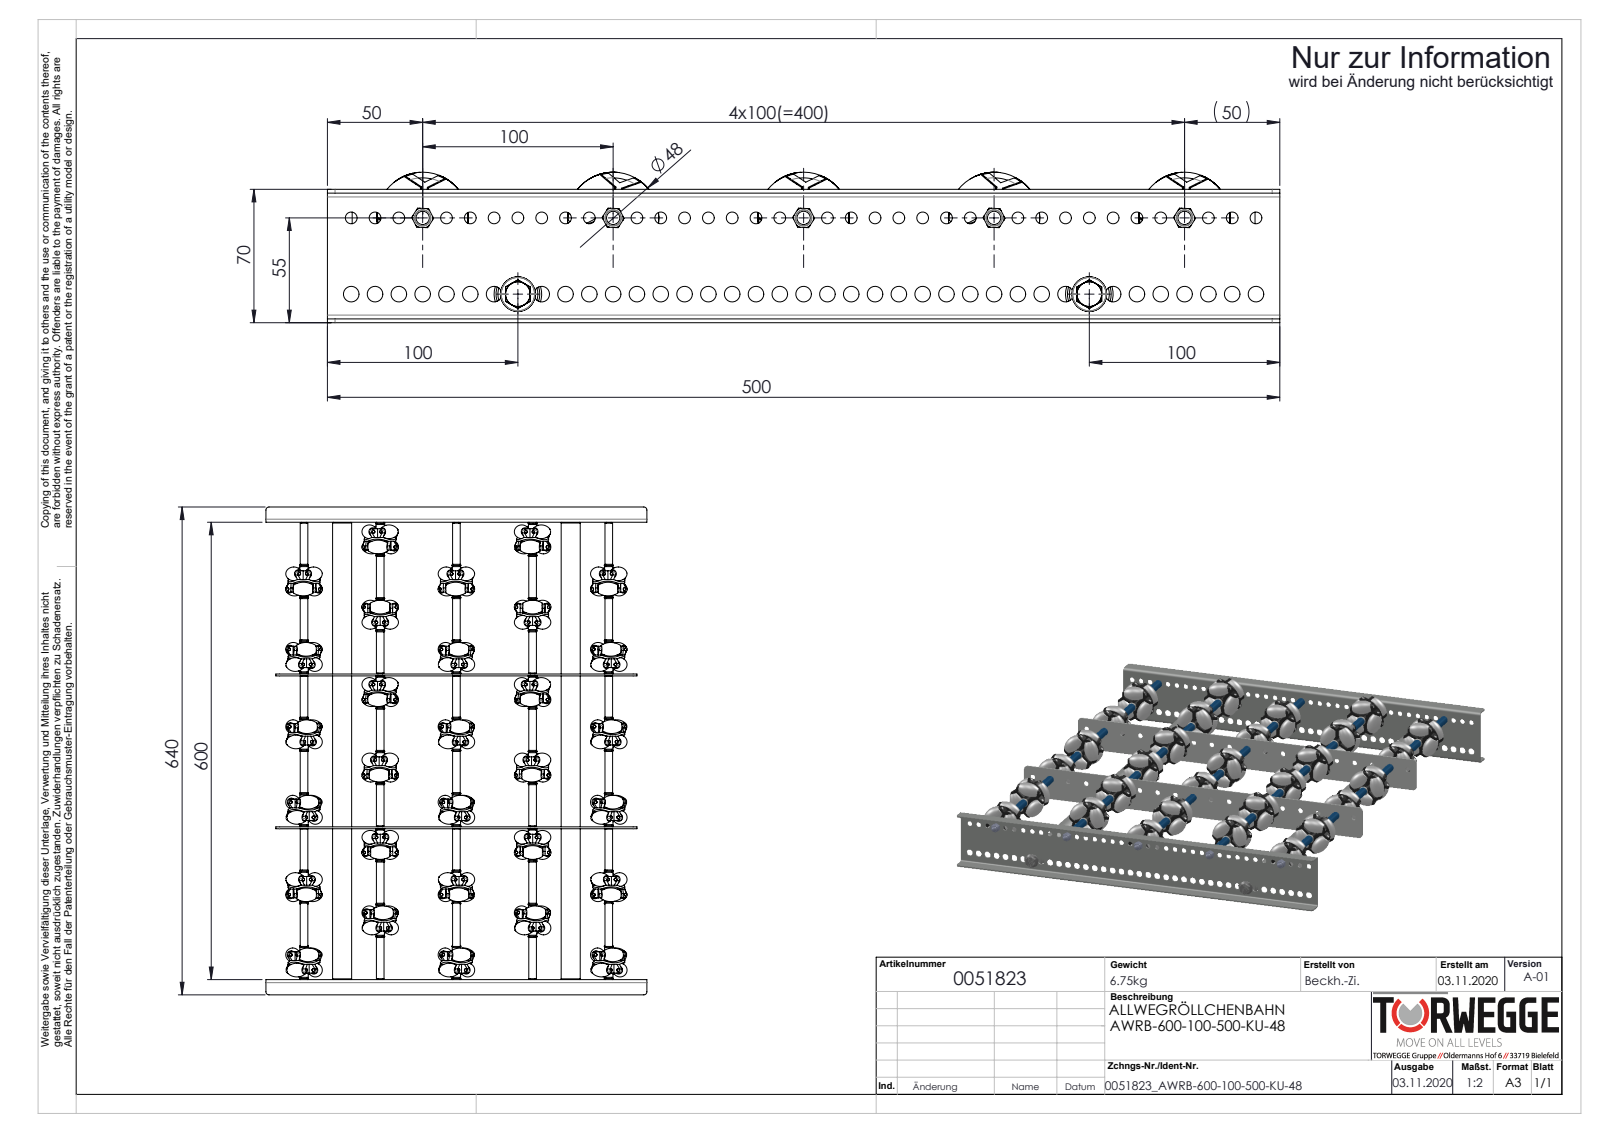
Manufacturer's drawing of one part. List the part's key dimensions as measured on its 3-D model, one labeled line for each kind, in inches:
Part name (STEP PRODUCT): AWR48_Röllchen; 0019730_Tragrollenrohr-Ø10x1,75KU_KFG_0019730_L=54; 0051823; AWR-Achse-für-Konfiguration_L600 (+8 more)
STEP written by: SolidWorks 2020 (AUTOMOTIVE_DESIGN)
Units: inches
Bodies: 509 solids, 9178 faces (3162 planar, 3622 cylindrical, 2394 other)
Overall size (bounding box): 25.197 × 19.685 × 3.11
Volume: 117.7 in³ · Surface area: 2 139 in²
Round holes (diameter × count): ⌀0.146 ×180, ⌀0.165 ×180, ⌀0.244 ×39, ⌀0.323 ×39, ⌀0.256 ×19, ⌀0.194 ×5, ⌀0.331 ×5, ⌀0.268 ×2, ⌀0.827 ×2
Round bosses / shafts (diameter × count): ⌀0.157 ×180, ⌀0.146 ×150, ⌀0.315 ×7, ⌀1.854 ×5, ⌀1.654 ×5, ⌀0.433 ×5, ⌀0.394 ×5, ⌀0.276 ×5
Partial cylindrical surfaces — rounded edges, fillets, slot ends (radius × count): R0.157 ×8, R0.079 ×4, R0.197 ×4
Main face-to-face distances: 0.079, 23.701, 7.894, 0.098, 2.677, 23.622, 23.78, 0.581, 0.118, 0.463
Hole centre spacings: 1.42, 1.419, 1.419, 0.492, 0.984, 1.476, 1.969, 2.461
